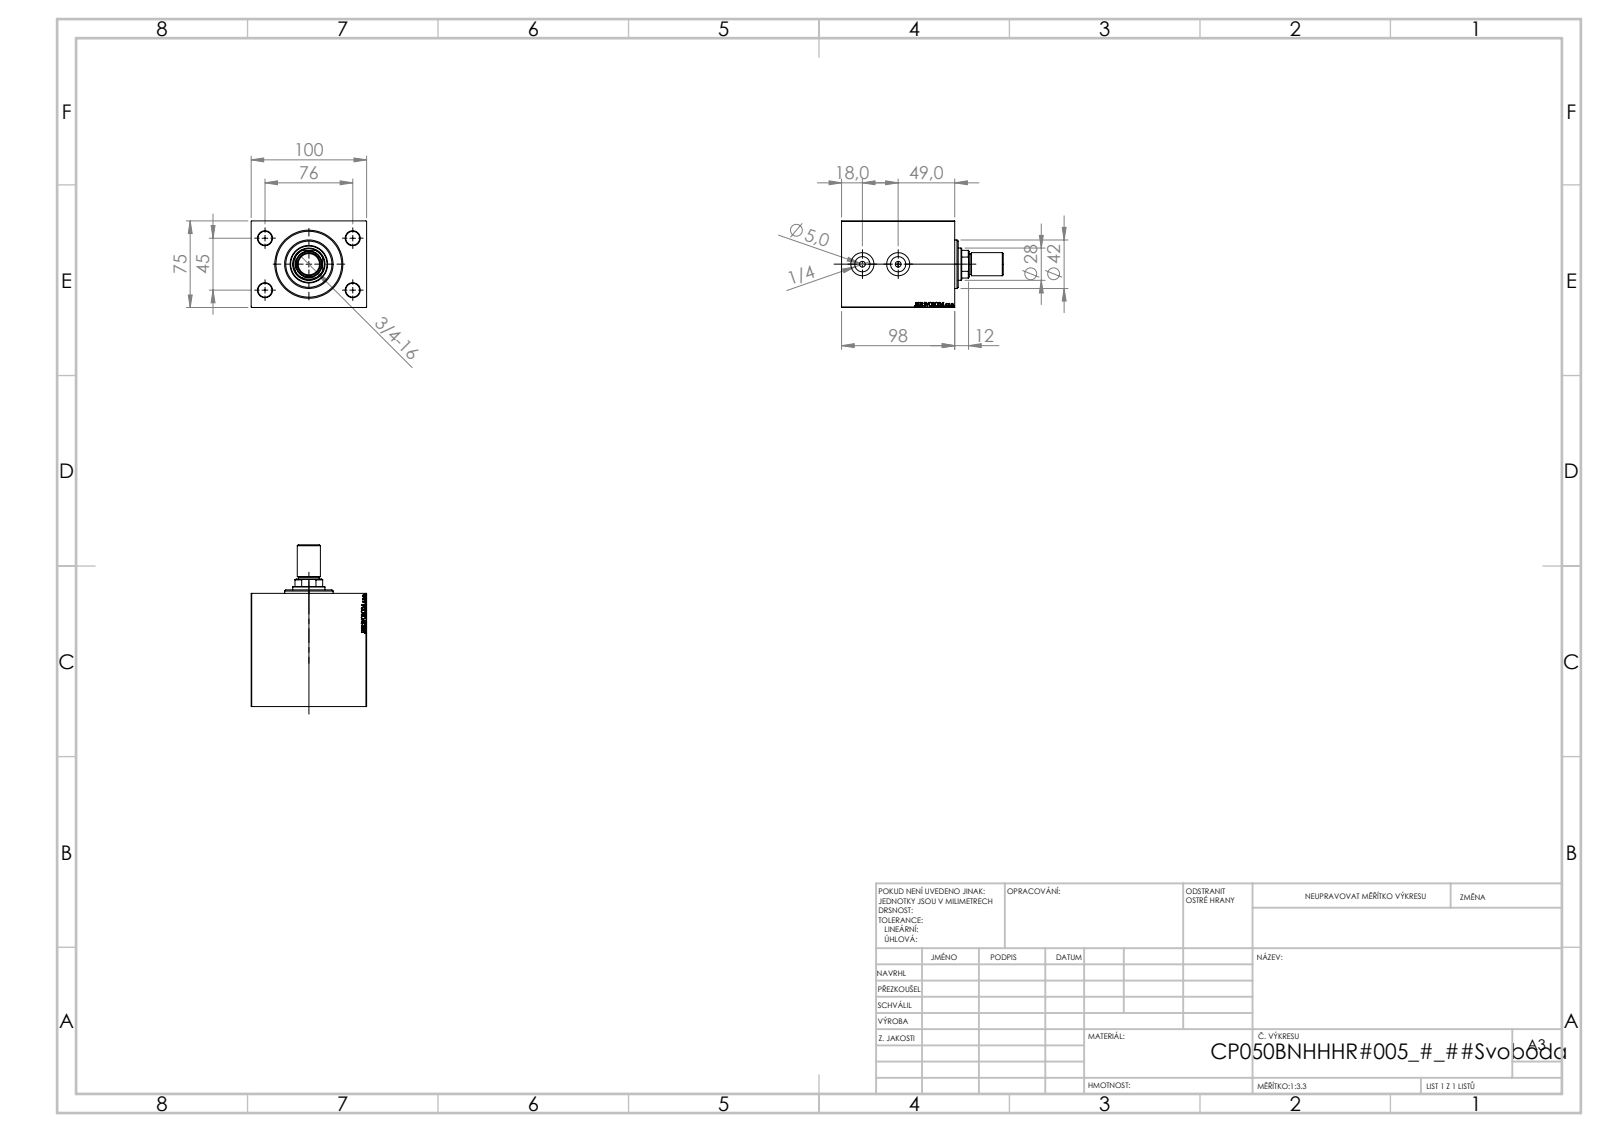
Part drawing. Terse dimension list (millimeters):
name: V450CP_B_VCP; V450CP_VC_B; V450CP_B; V450CM_MALE_METRIC
written by: SolidWorks 2019 (CONFIG_CONTROL_DESIGN)
unit: mm
bodies: 4 solids, 918 faces (410 planar, 72 cylindrical, 436 other)
size: 140 × 100 × 75
volume: 714 384 mm³; area: 106 349 mm²
holes: 4× ⌀12, 2× ⌀4, 2× ⌀5, 2× ⌀9.73, 2× ⌀13.16, 2× ⌀15, 2× ⌀20, 1× ⌀18.5, 1× ⌀28, 1× ⌀31.5, 1× ⌀32.5, 1× ⌀50
bosses: 1× ⌀42, 1× ⌀20, 1× ⌀18
rounds: 1× R13.5
face distances: 75, 100, 98, 49, 14, 84, 44, 5, 35, 30
hole spacings: 44.16, 45, 76, 88.32, 31, 42.55
